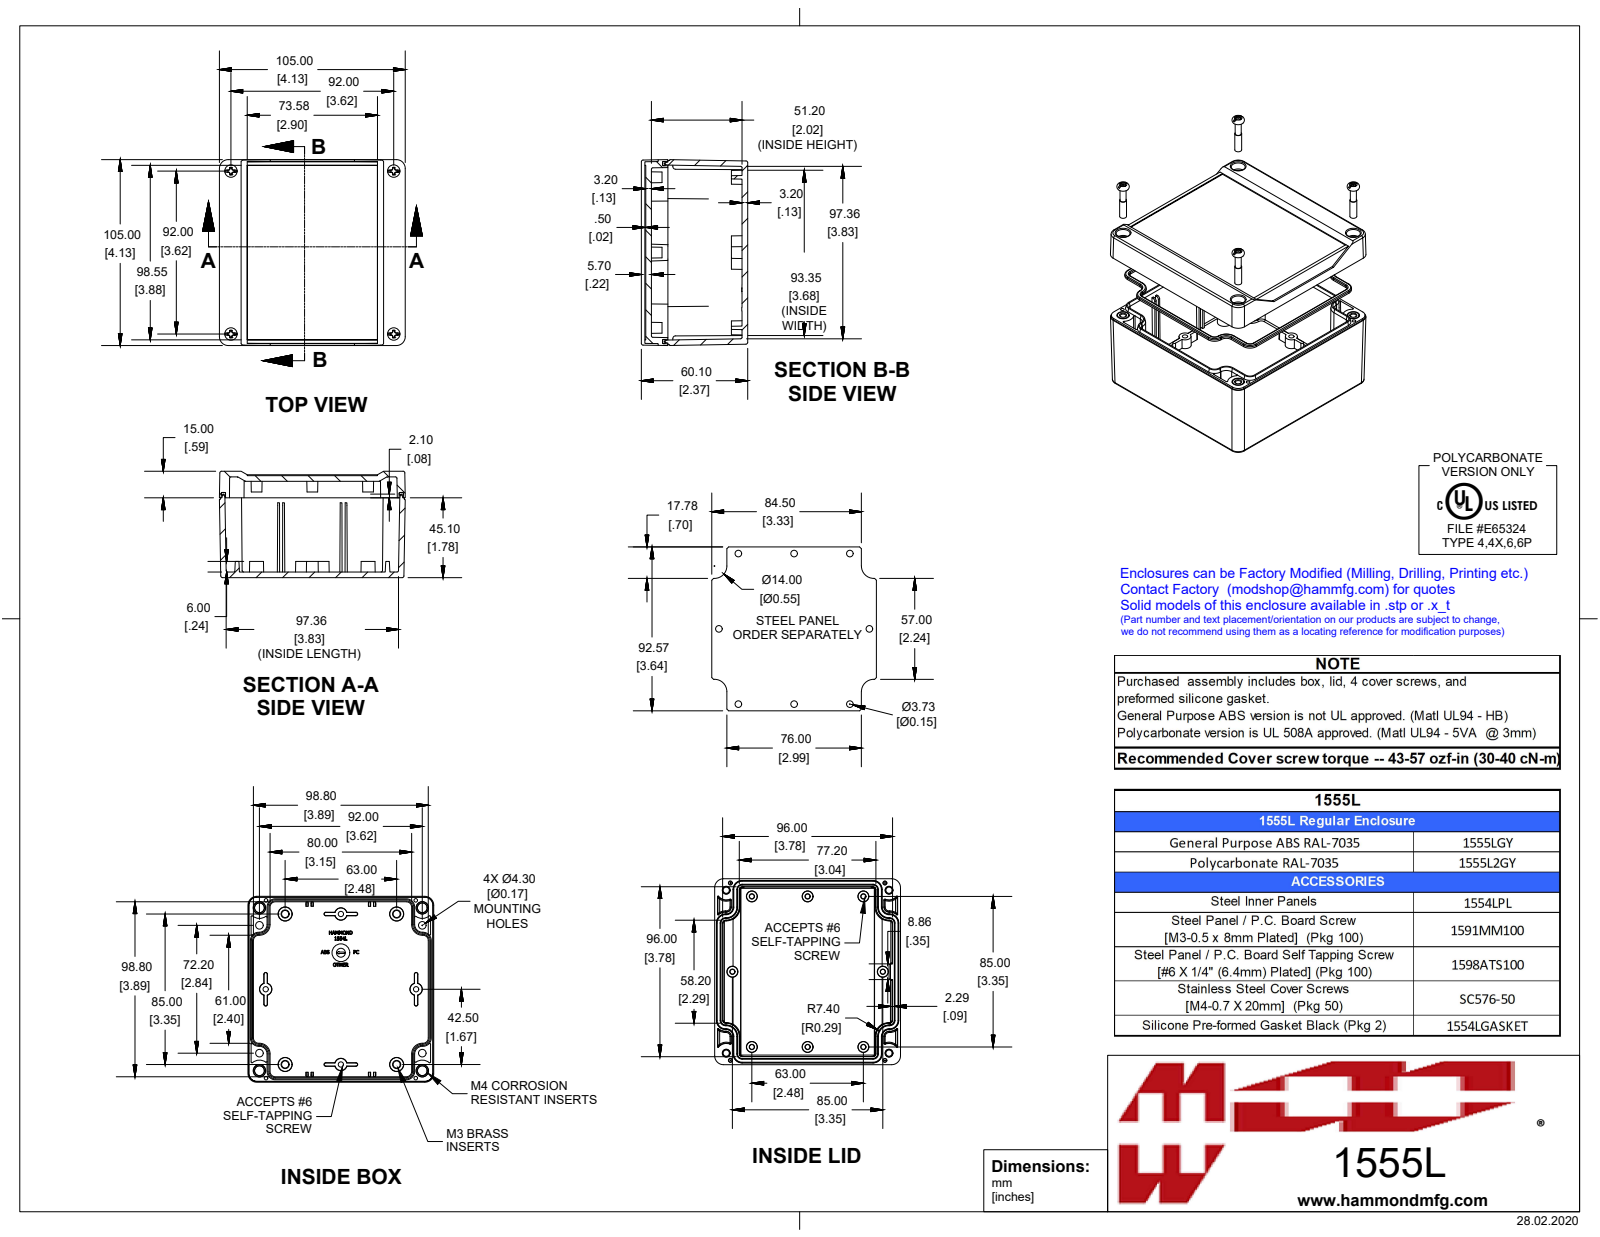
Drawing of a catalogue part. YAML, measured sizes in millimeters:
part_name: "1555L2GY"
step_written_by: "SolidWorks 2019 (AUTOMOTIVE_DESIGN)"
units: millimeters
bodies: {solids: 15, faces: 1921, planar: 646, cylindrical: 381, other: 894}
overall_size: [105, 105, 60.1]
volume: 158300
surface_area: 113200
round_holes:
  - {diameter: 2.5, count: 4}
  - {diameter: 3.3, count: 4}
  - {diameter: 4.6, count: 4}
  - {diameter: 3.5, count: 3}
round_bosses_or_shafts:
  - {diameter: 6.4, count: 4}
  - {diameter: 5.5, count: 4}
  - {diameter: 5.3, count: 4}
  - {diameter: 4.8, count: 4}
  - {diameter: 3.9, count: 4}
  - {diameter: 3.9, count: 4}
  - {diameter: 3.8, count: 4}
  - {diameter: 3.4, count: 4}
partial_cylinders:
  - {radius: 0.5, count: 26}
  - {radius: 0.3, count: 22}
  - {radius: 1, count: 12}
  - {radius: 0.8, count: 10}
  - {radius: 2.6, count: 8}
  - {radius: 5, count: 8}
  - {radius: 5.1, count: 8}
  - {radius: 3, count: 4}
face_to_face_distances: [3.2, 54.4, 3.1, 57.6, 51.2, 105, 101.9, 2.5, 100.5, 56.9]
hole_center_spacings: [14.9, 77.6, 89.7, 92, 117.6, 63, 85, 105.8]
